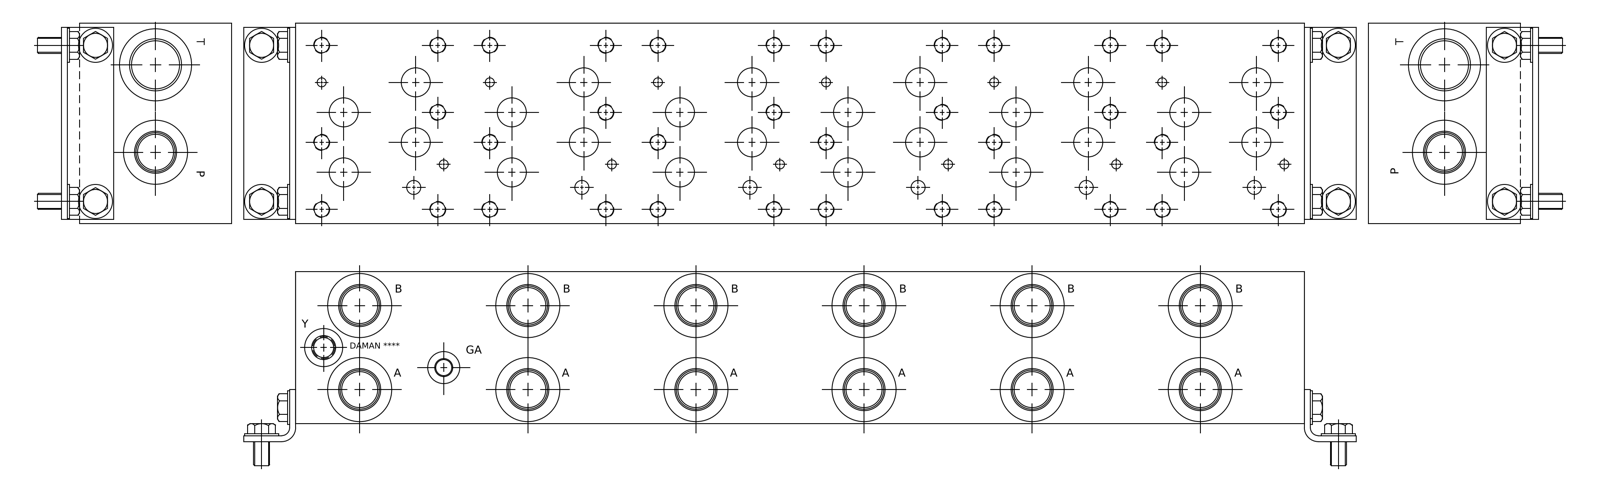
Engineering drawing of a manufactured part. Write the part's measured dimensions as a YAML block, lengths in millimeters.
part_name: "Part_AD08P065S_3D"
step_written_by: "Autodesk Inventor 2019 (AUTOMOTIVE_DESIGN)"
units: millimeters
bodies: {solids: 1, faces: 1136, planar: 505, cylindrical: 224, other: 407}
overall_size: [800.1, 158.75, 120.65]
volume: 14520000
surface_area: 621777
round_holes:
  - {diameter: 10.72, count: 39}
  - {diameter: 12.7, count: 38}
  - {diameter: 23.01, count: 23}
  - {diameter: 31.27, count: 13}
  - {diameter: 33.76, count: 13}
  - {diameter: 49.12, count: 13}
  - {diameter: 7.14, count: 12}
  - {diameter: 28.57, count: 12}
  - {diameter: 33.35, count: 12}
  - {diameter: 35.51, count: 12}
  - {diameter: 11.13, count: 5}
  - {diameter: 33.34, count: 2}
face_to_face_distances: [120.65, 158.75, 0.79, 800.1, 157.96, 799.31, 798.52, 19.84, 19.05, 90.42]
hole_center_spacings: [133.35, 266.7, 400.05, 270.92, 191.98, 533.4, 61.92, 210.9]
